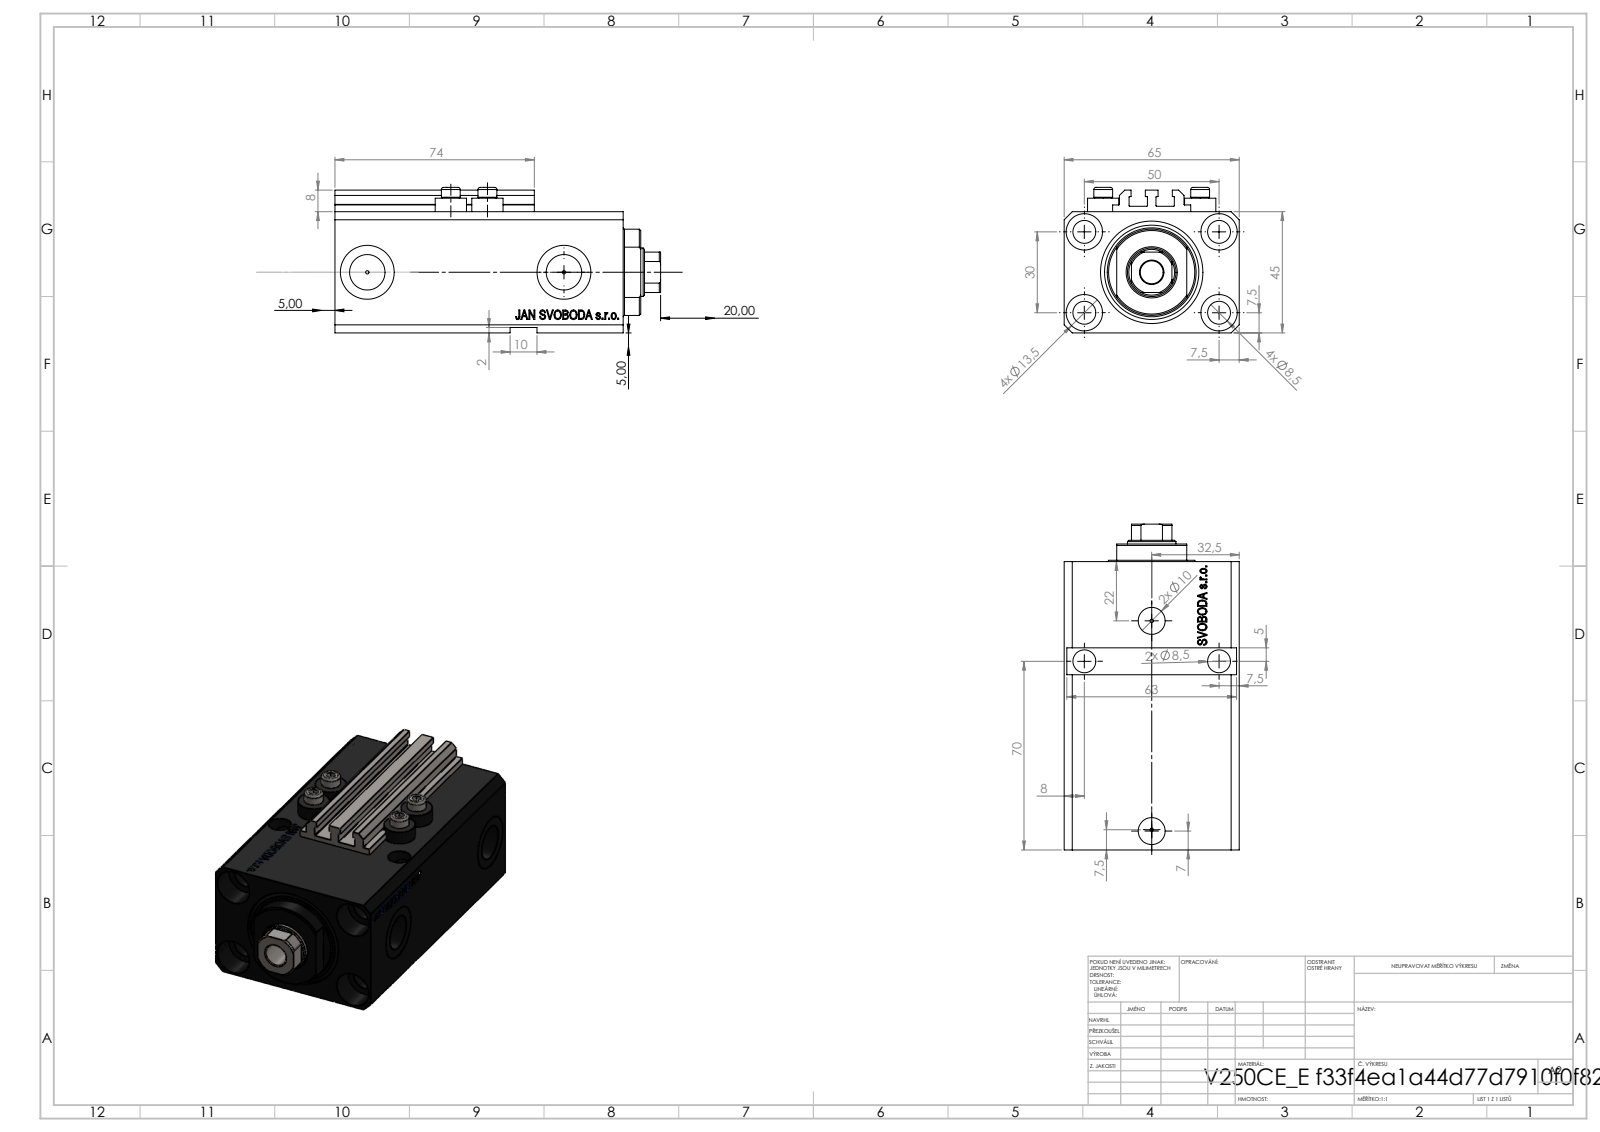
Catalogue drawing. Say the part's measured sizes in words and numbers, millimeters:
The part is named "V250CE_VC_E; ALLEN BOLT V250CE; V250CE_E_Body; V250CE_C_VCP". Its 3-D file was written by "SolidWorks 2019 (CONFIG_CONTROL_DESIGN)". It is 8 solids with 1103 faces: 515 planar, 158 cylindrical and 430 other. Overall it measures 121 by 65 by 54 millimeters. Its volume is 269 783 cubic millimeters and its surface area 78 013 square millimeters. Round holes: 9 of diameter 8.5, 4 of diameter 1.25, 4 of diameter 4, 4 of diameter 13.5, 2 of diameter 10, 2 of diameter 13.16, 2 of diameter 20, 1 of diameter 18, 1 of diameter 25, 1 of diameter 38. Round bosses or shafts: 4 of diameter 11.6, 4 of diameter 7. Partial cylindrical surfaces (rounded edges, fillets, slot ends): 10 of radius 0.2, 1 of radius 8.5, 1 of radius 16. The main face-to-face distances are 45, 65, 93, 2, 14, 47, 107, 2.5, 10, 6.9. The hole center spacings are 29.15, 50, 13.6, 14.76, 15.12, 27.51, 27.89, 30.
